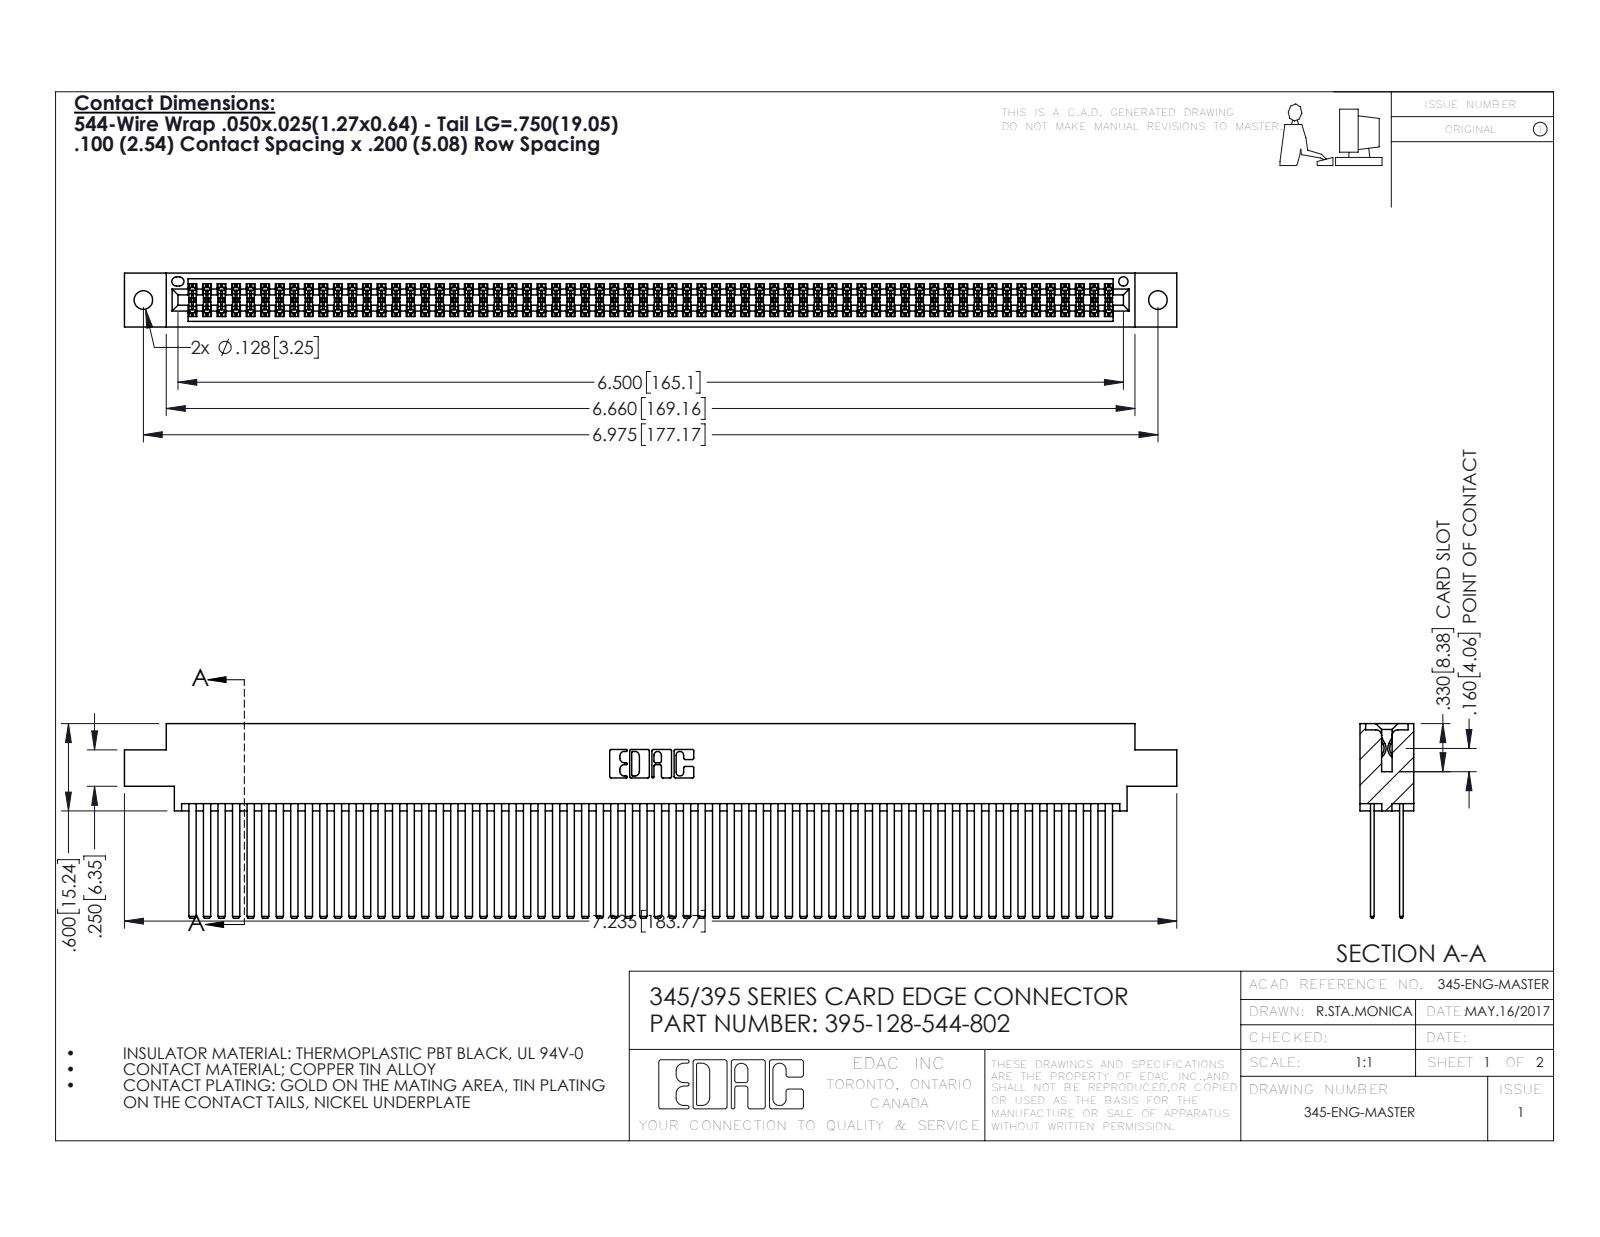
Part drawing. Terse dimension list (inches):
name: 395-128-544-802; 345 Part_0.170 Offset - 0.128 Dia; 345-292-001_345-293-144
written by: SolidWorks 2016 (CONFIG_CONTROL_DESIGN)
unit: in
bodies: 129 solids, 5762 faces (3796 planar, 1966 cylindrical, 0 other)
size: 7.235 × 1.337 × 0.37
volume: 1.202 in³; area: 53.75 in²
holes: 2× ⌀0.128, 1× ⌀0.064
rounds: 192× R0.006, 22× R0.01, 6× R0.007, 6× R0.031, 3× R0.026, 2× R0.014, 2× R0.019, 2× R0.022
face distances: 0.2, 0.025, 0.298, 0.072, 0.098, 0.272, 0.225, 0.175, 0.37, 0.15
hole spacings: 0.27, 6.739, 6.975
